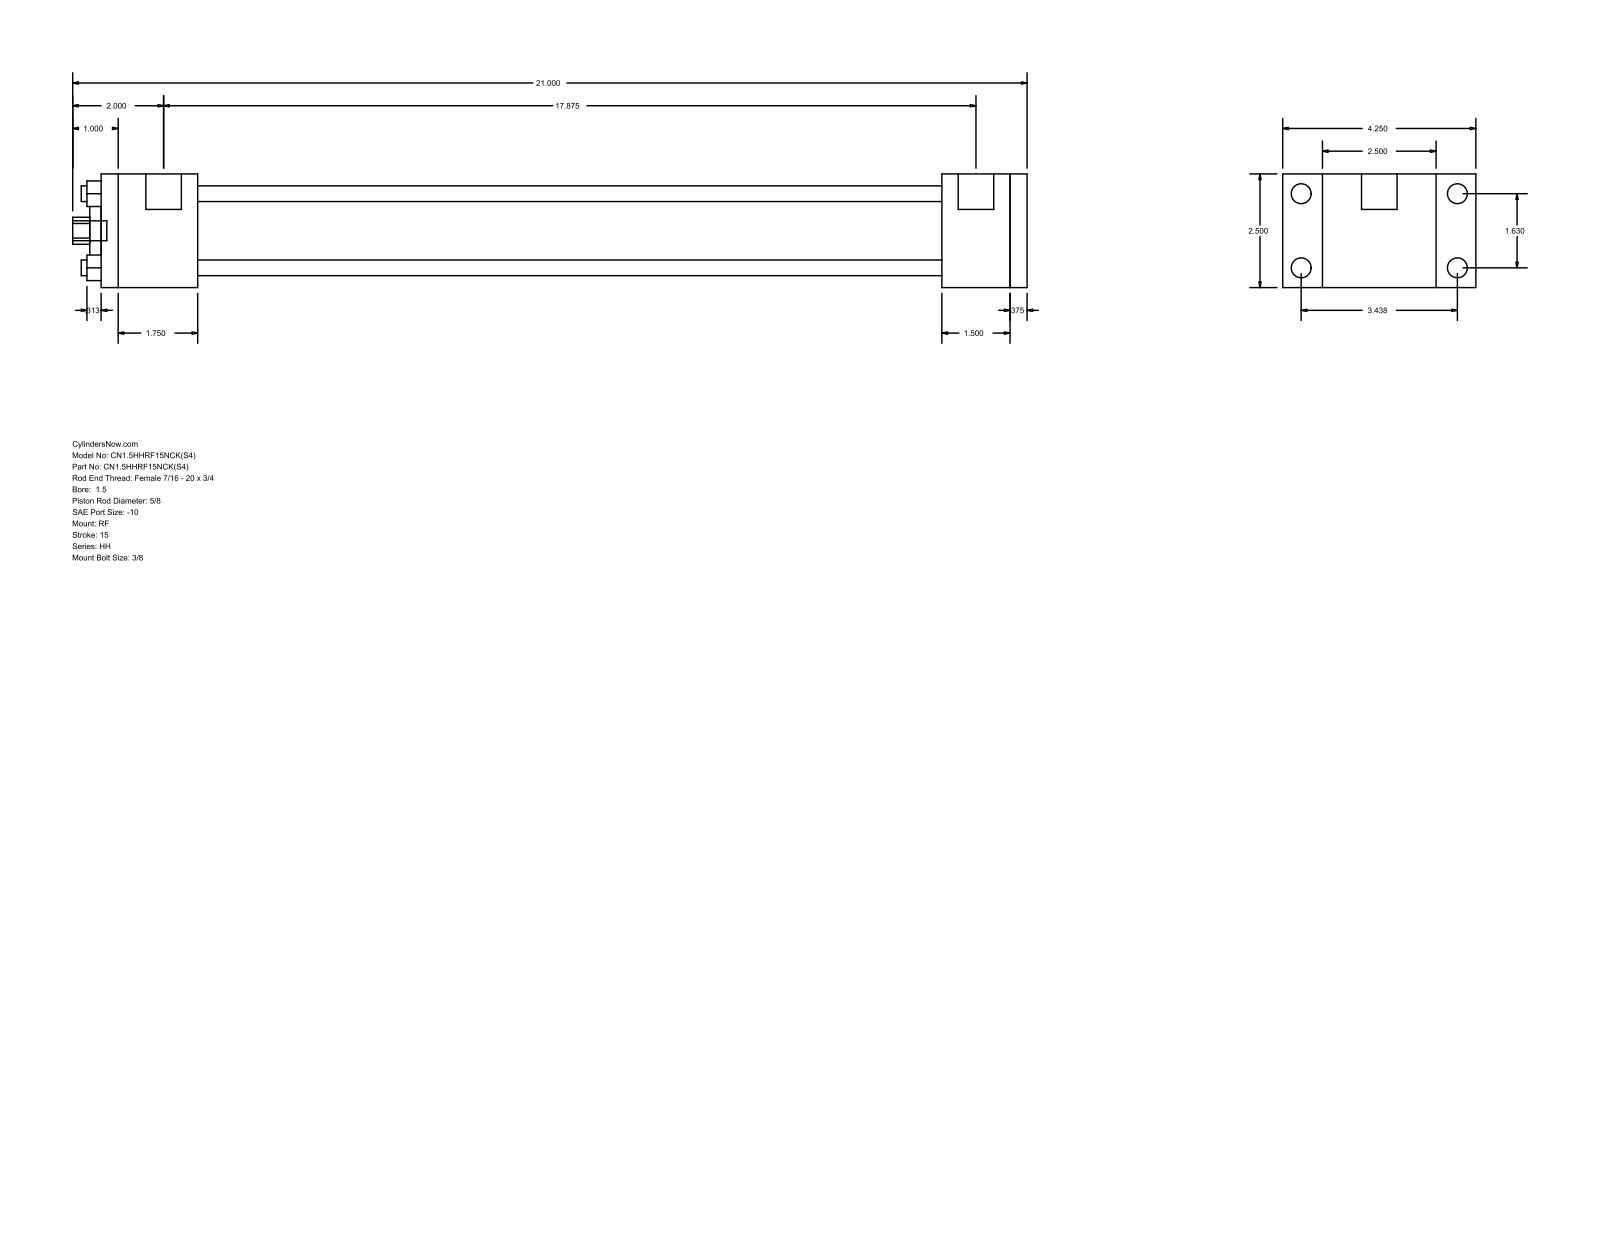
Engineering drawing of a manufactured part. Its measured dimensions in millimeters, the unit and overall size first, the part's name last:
Units: millimetres
Overall size (bounding box): 533.4 × 107.95 × 63.5
Round holes (diameter × count): ⌀8.76 ×4, ⌀15.88 ×1, ⌀28.57 ×1, ⌀44.45 ×1
Round bosses / shafts (diameter × count): ⌀11.13 ×4, ⌀5.56 ×4, ⌀19.84 ×2, ⌀11.11 ×1
Partial cylindrical surfaces — rounded edges, fillets, slot ends (radius × count): R7.54 ×1
Main face-to-face distances: 63.5, 517.52, 9.52, 508, 47.63, 53.97, 469.89, 415.92, 454.03, 463.55
Hole centre spacings: 29.27, 41.4, 58.55
Bodies: 0 solids, 92 faces (64 planar, 28 cylindrical, 0 other)
Part name (STEP PRODUCT): HH_RF__0150_0.625
STEP written by: GSSL Pune (CONFIG_CONTROL_DESIGN)
